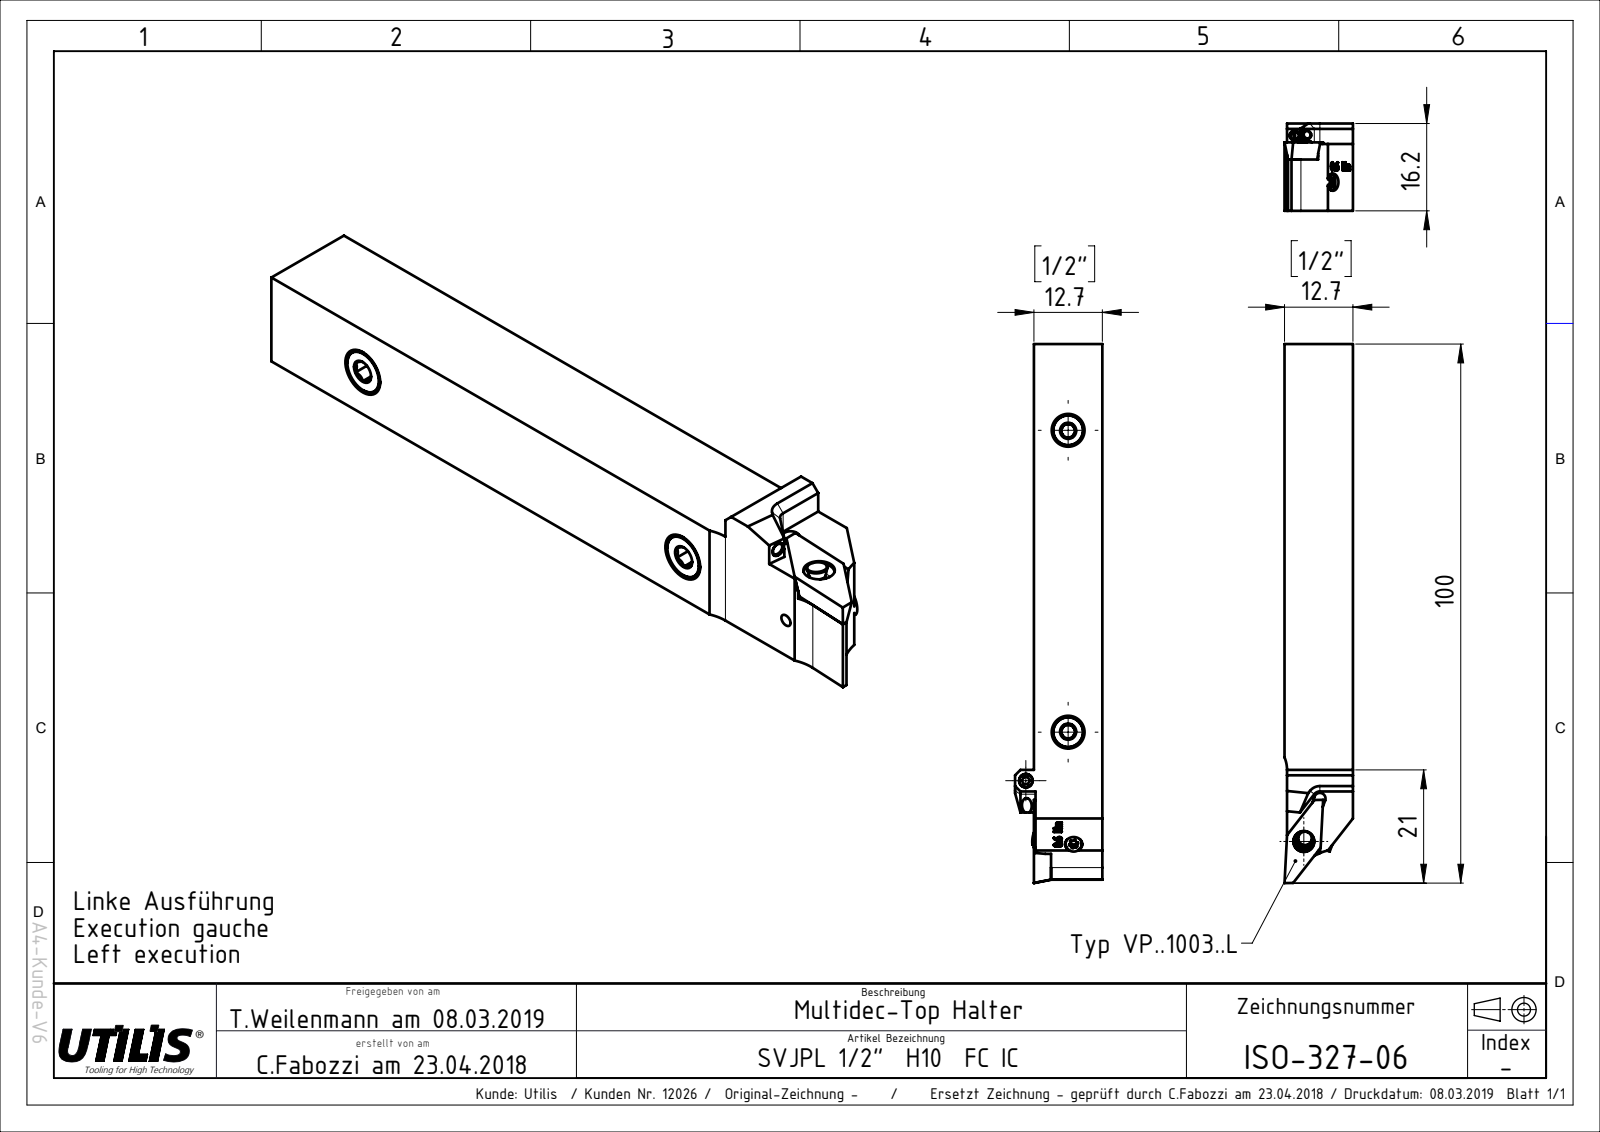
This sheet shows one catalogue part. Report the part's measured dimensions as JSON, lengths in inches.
{"part_name": "ISO-327-06", "step_written_by": "SolidWorks 2017 (AUTOMOTIVE_DESIGN)", "units": "inches", "bodies": {"solids": 1, "faces": 124, "planar": 63, "cylindrical": 8, "other": 53}, "overall_size": [3.937, 0.638, 0.5], "volume_in3": 0.931, "surface_area_in2": 8.285, "round_holes": [[0.126, 1]], "partial_cylinders_radius": [[0.041, 1], [0.052, 1], [0.236, 1], [0.24, 1], [0.347, 1]], "face_to_face_distances": [0.5, 0.019, 0.481, 0.488, 3.11, 0.638, 0.15, 0.138, 0.079, 0.157]}
